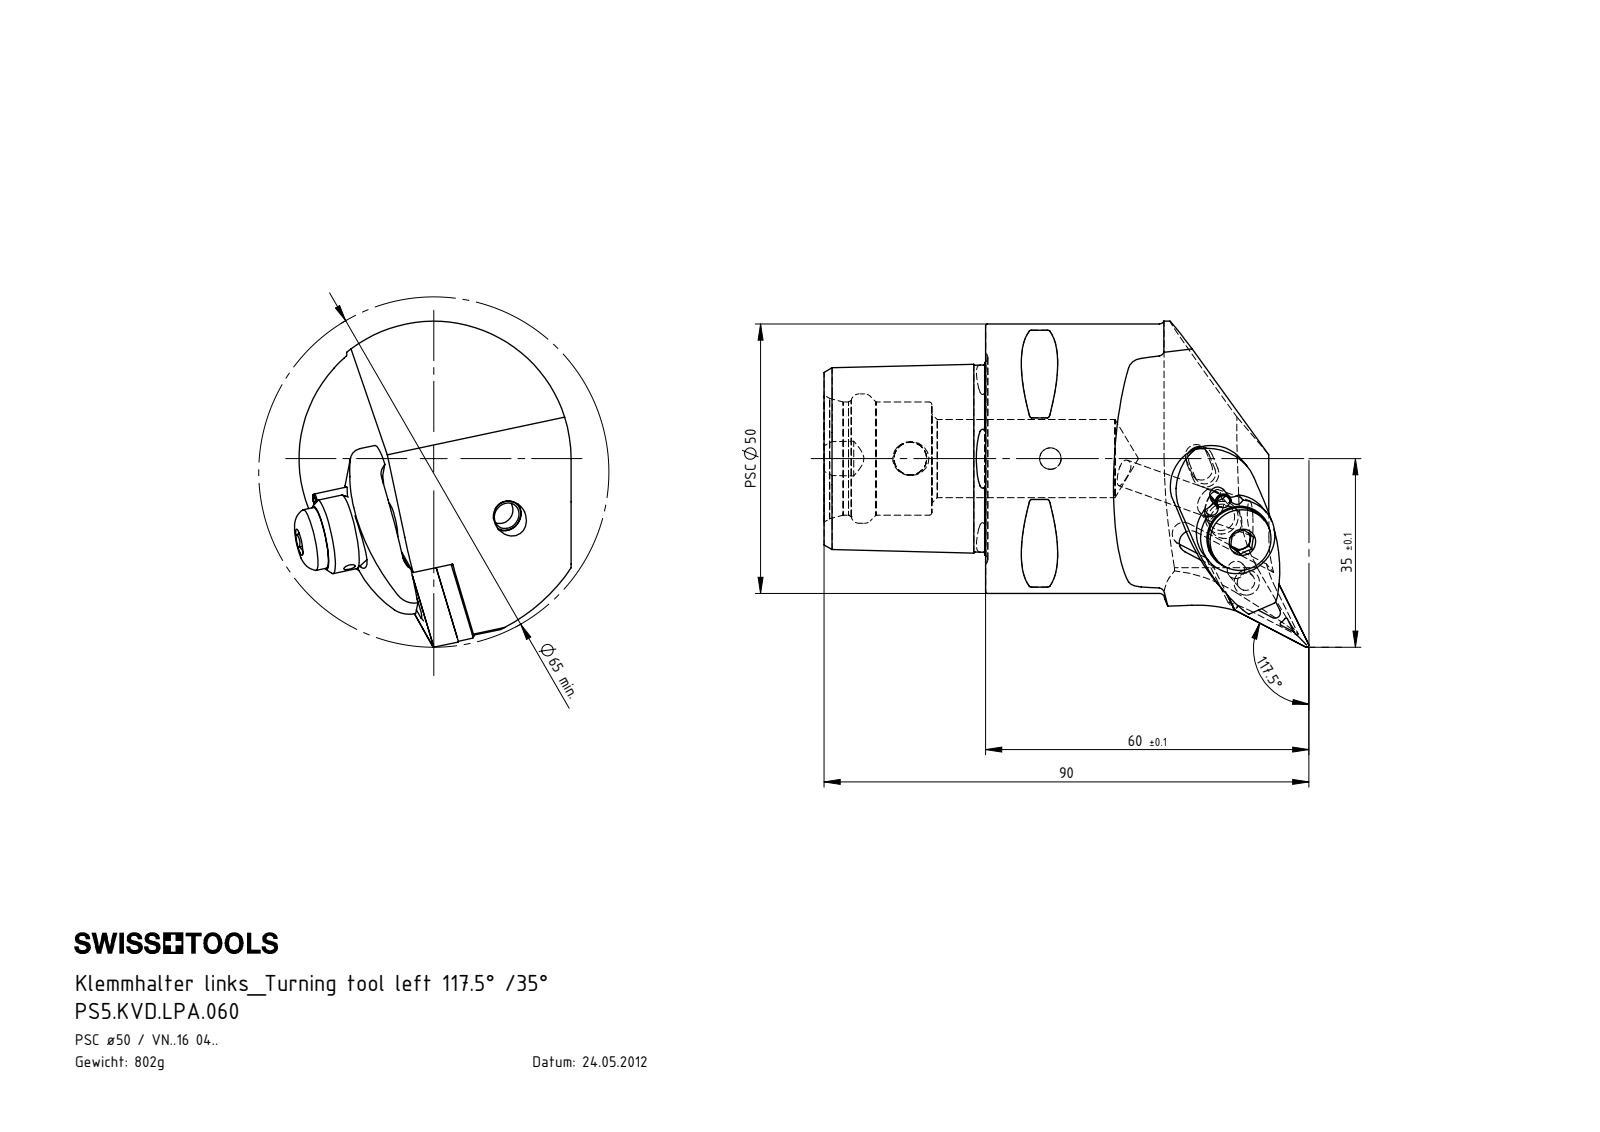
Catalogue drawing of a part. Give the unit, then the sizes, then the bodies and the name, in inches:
Units: inches
Overall size (bounding box): 3.543 × 2.382 × 2.021
Round holes (diameter × count): ⌀0.079 ×3, ⌀0.197 ×3, ⌀0.276 ×2, ⌀0.094 ×1, ⌀0.118 ×1, ⌀0.13 ×1, ⌀0.15 ×1, ⌀0.157 ×1, ⌀0.195 ×1, ⌀0.236 ×1, ⌀0.24 ×1, ⌀0.244 ×1
Round bosses / shafts (diameter × count): ⌀0.236 ×2, ⌀0.157 ×2, ⌀0.118 ×2, ⌀1.969 ×1, ⌀0.551 ×1, ⌀0.453 ×1, ⌀0.268 ×1, ⌀0.244 ×1
Partial cylindrical surfaces — rounded edges, fillets, slot ends (radius × count): R0.02 ×10, R0.013 ×6, R0.023 ×6, R0.016 ×4, R0.059 ×3, R0.079 ×2, R0.118 ×2, R0.157 ×2
Main face-to-face distances: 1.181, 0.175, 0.375, 0.363, 0.227, 0.052, 0.3, 0.755, 0.352, 0.125
Hole centre spacings: 0.563, 0.284, 0.284, 0.848, 0.039, 0.039, 0.322, 0.323
Volume: 6.08 in³ · Surface area: 37.33 in²
Bodies: 11 solids, 437 faces (100 planar, 136 cylindrical, 201 other)
Part name (STEP PRODUCT): WCB-ER2.001.009_A; WVD-ER2.101.003_A; WCC-ER3.102.024_C; WCC-ER4.103.032_A (+7 more)
STEP written by: SolidWorks 2017 (AUTOMOTIVE_DESIGN)
